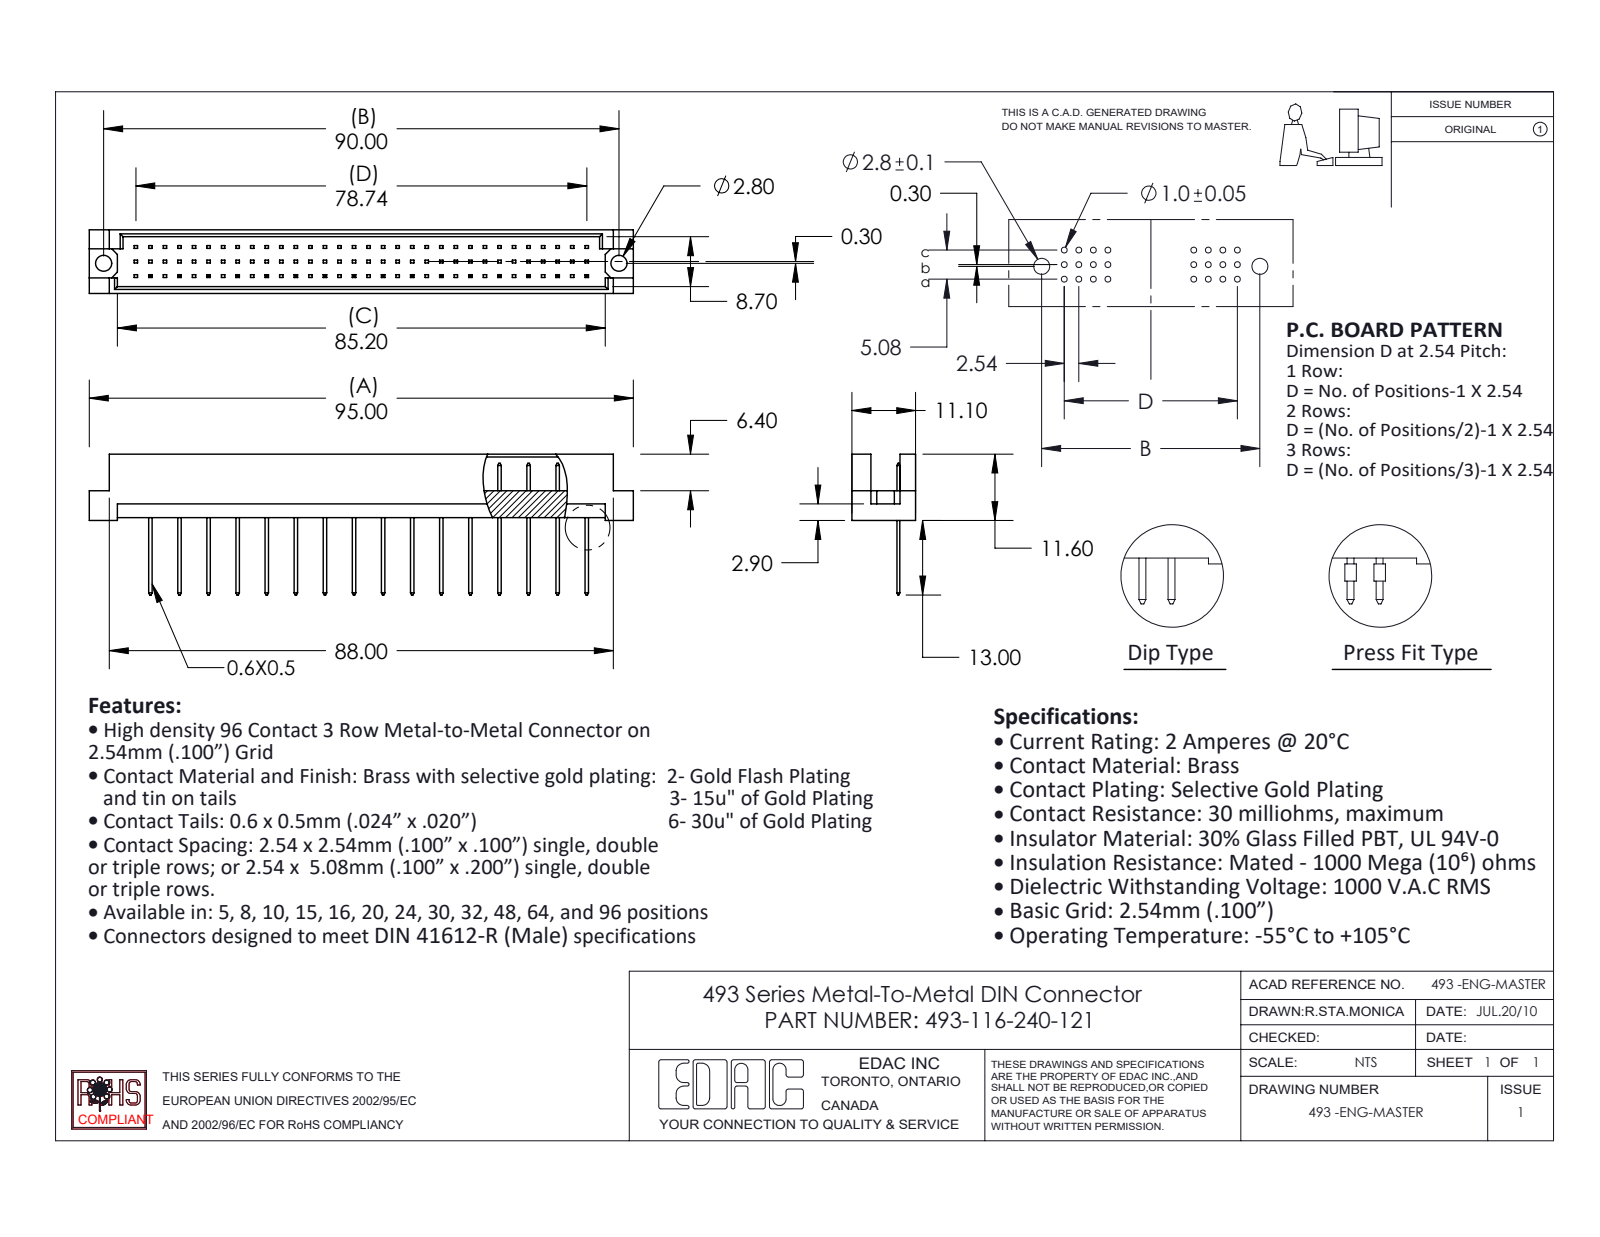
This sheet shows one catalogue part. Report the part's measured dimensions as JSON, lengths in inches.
{"part_name": "493-290_40; 493-116-240-121; 493 Part_96", "step_written_by": "SolidWorks 2020 (CONFIG_CONTROL_DESIGN)", "units": "inches", "bodies": {"solids": 17, "faces": 660, "planar": 656, "cylindrical": 4, "other": 0}, "overall_size": [3.74, 0.969, 0.437], "volume_in3": 0.352, "surface_area_in2": 11.28, "round_holes": [[0.11, 2]], "face_to_face_distances": [0.047, 0.39, 0.437, 0.343, 0.185, 0.02, 0.2, 0.109, 0.128, 0.309], "hole_center_spacings": [3.543]}
